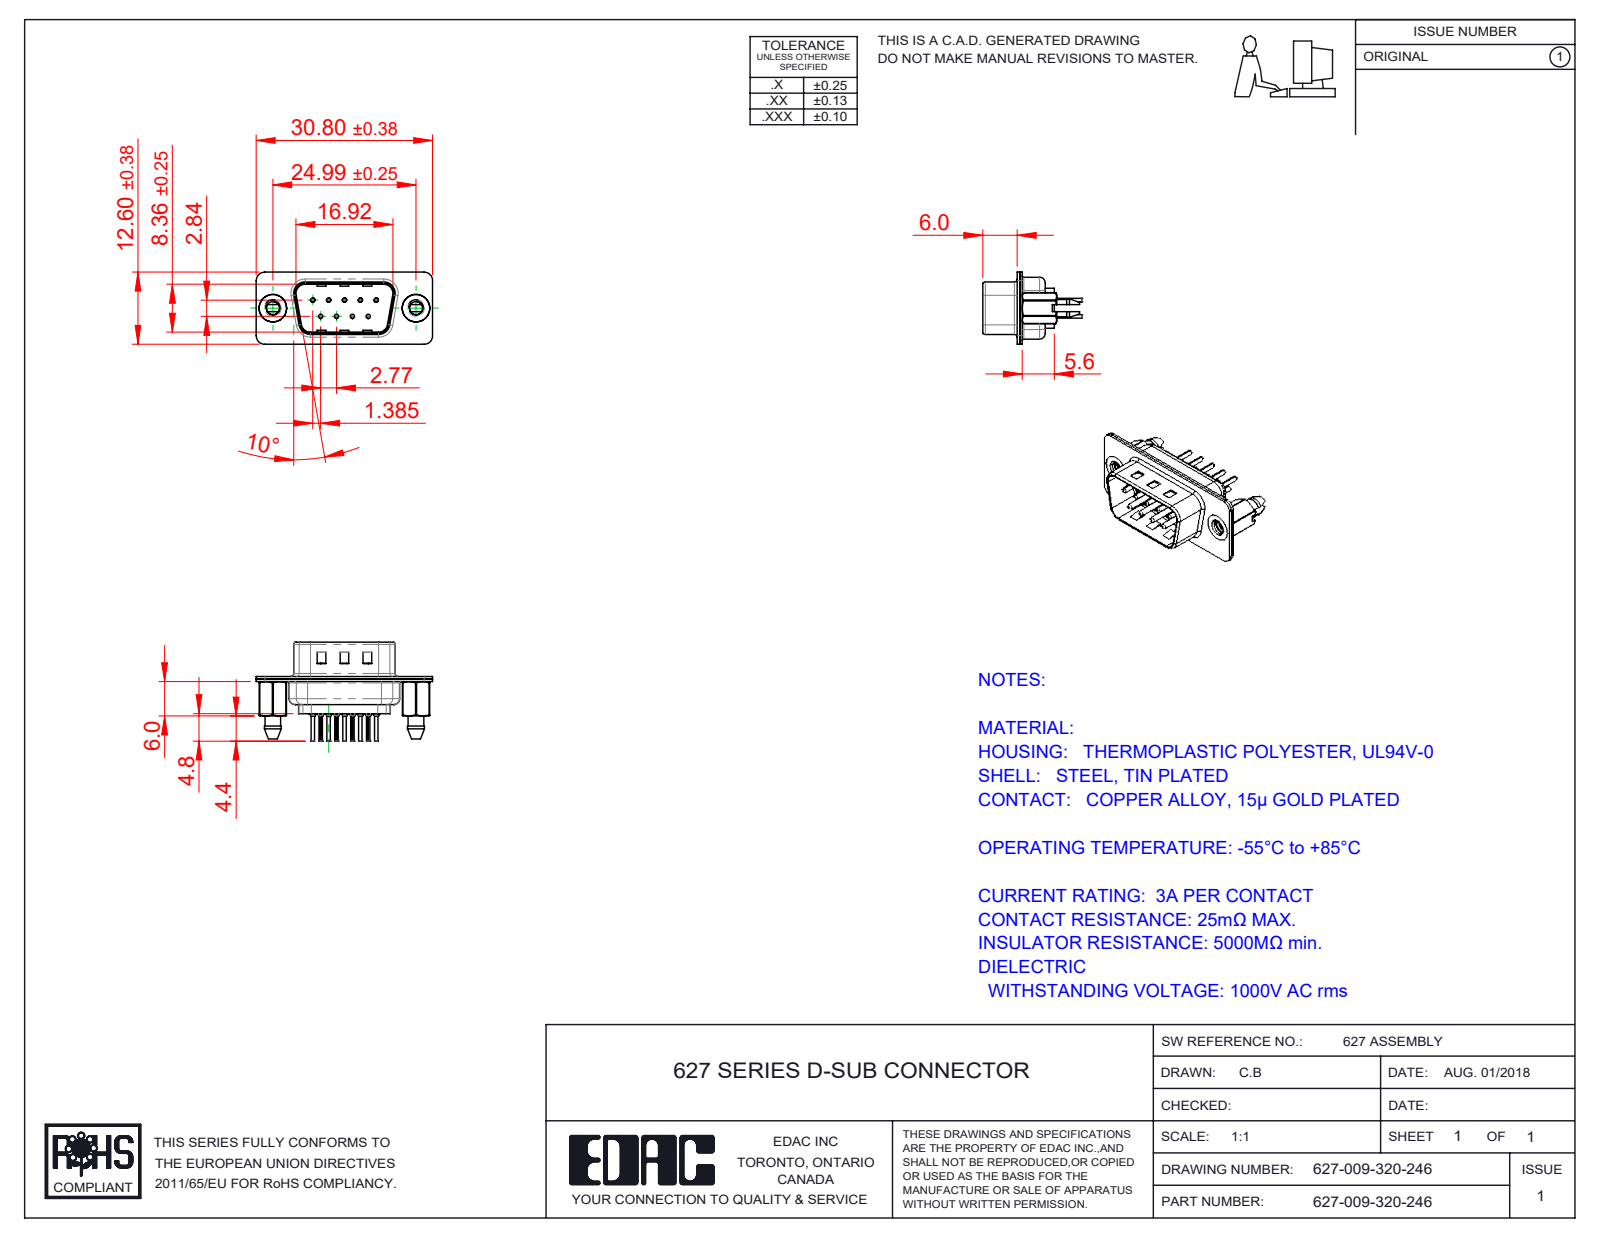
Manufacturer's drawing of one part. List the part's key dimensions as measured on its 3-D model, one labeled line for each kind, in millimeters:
Part name (STEP PRODUCT): 627 Housing_09 LP; 627 Shell Rear_09 Contacts; 627-009-320-046; 627 Contact Row 2_20L (+3 more)
STEP written by: SolidWorks 2020 (CONFIG_CONTROL_DESIGN)
Units: millimetres
Bodies: 14 solids, 1260 faces (355 planar, 494 cylindrical, 411 other)
Overall size (bounding box): 30.8 × 17.3 × 12.6
Volume: 1 427 mm³ · Surface area: 4 226 mm²
Round holes (diameter × count): ⌀0.2 ×9, ⌀0.35 ×9, ⌀1.1 ×9, ⌀1.6 ×9, ⌀2.26 ×2, ⌀4 ×2, ⌀4.8 ×2
Round bosses / shafts (diameter × count): ⌀2 ×9, ⌀1.5 ×9, ⌀0.75 ×9, ⌀0.6 ×9, ⌀4.9 ×2
Partial cylindrical surfaces — rounded edges, fillets, slot ends (radius × count): R1.5 ×20, R0.1 ×18, R2 ×12, R1.6 ×10, R0.5 ×8, R0.25 ×4, R0.6 ×4, R0.65 ×4
Main face-to-face distances: 0.45, 0.4, 0.9, 0.82, 9.58, 1.4, 8.76, 6.5, 0.5, 1.5
Hole centre spacings: 3.16, 2.77, 5.54, 5.03, 5.04, 8.31, 7.48, 7.49
